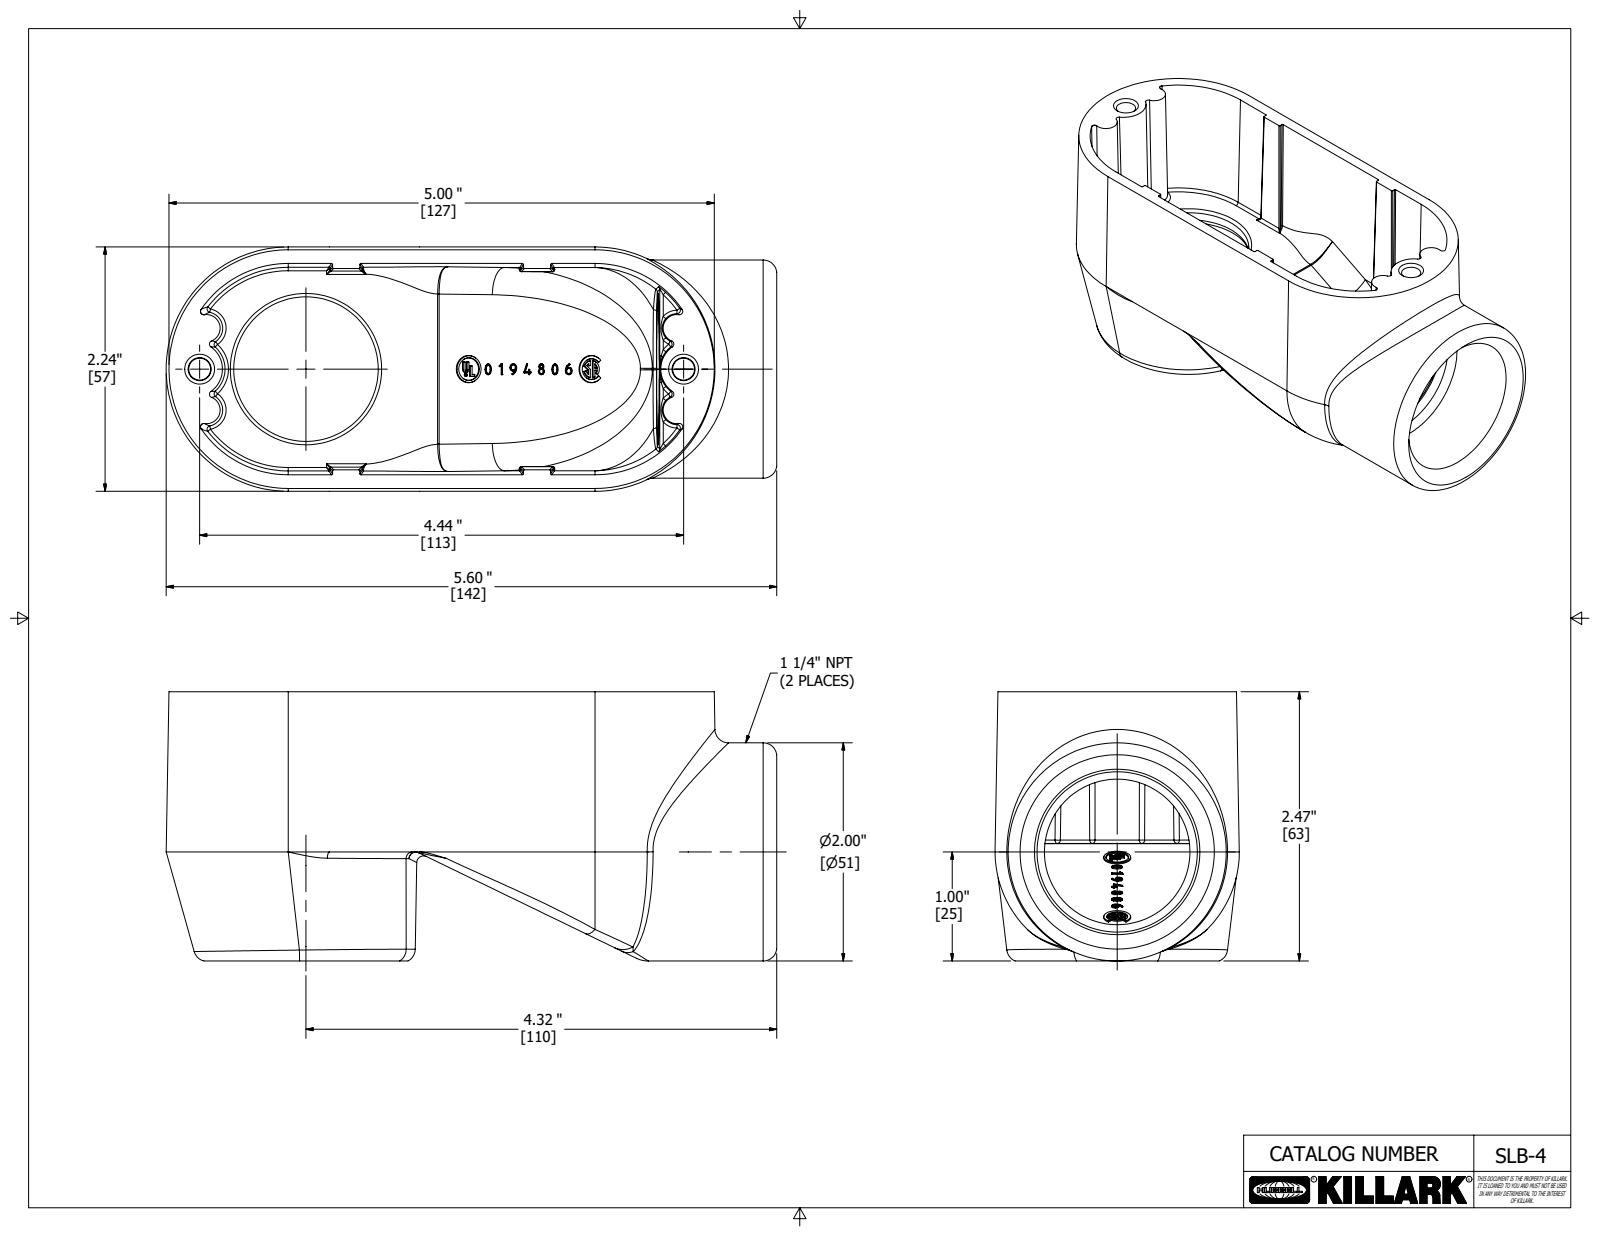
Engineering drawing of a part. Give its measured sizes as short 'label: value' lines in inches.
name: 0194806 -2
written by: Autodesk Inventor 2020 (AUTOMOTIVE_DESIGN)
unit: in
bodies: 1 solid, 428 faces (115 planar, 45 cylindrical, 268 other)
size: 5.599 × 2.469 × 2.24
volume: 7.597 in³; area: 75.09 in²
holes: 1× ⌀1.334
bosses: 1× ⌀2
rounds: 18× R0.01, 9× R0.031, 3× R0.25, 2× R0.925, 2× R1, 1× R0.062
face distances: 0.157, 1.391, 0.078, 1.469, 1.75, 0.969, 0.891, 0.5, 1.259, 3.009
